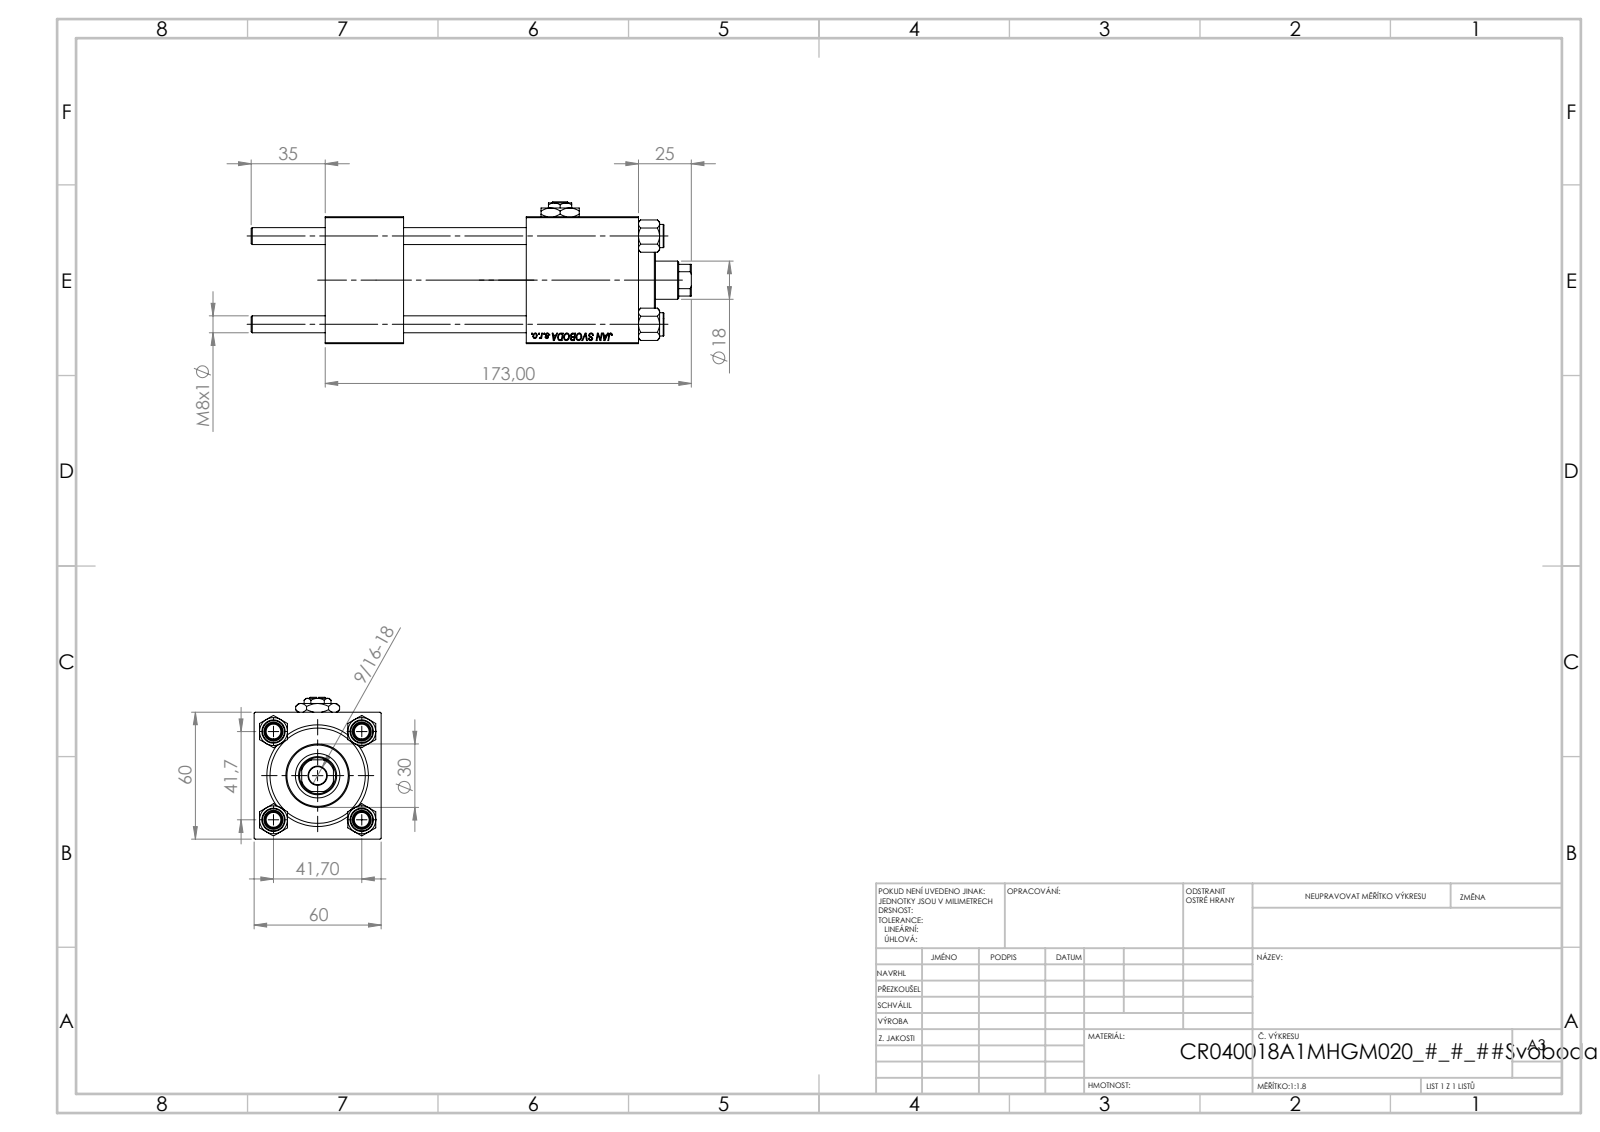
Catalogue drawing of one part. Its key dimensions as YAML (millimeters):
part_name: "V215CR_BODY_A; NUT_M5; Zatka_pro_OIL_PORT; V215_VC_A (+2 more)"
step_written_by: "SolidWorks 2019 (CONFIG_CONTROL_DESIGN)"
units: millimeters
bodies: {solids: 12, faces: 1183, planar: 545, cylindrical: 82, other: 556}
overall_size: [208, 67, 60]
volume: 412009
surface_area: 115273
round_holes:
  - {diameter: 8, count: 4}
  - {diameter: 7, count: 2}
  - {diameter: 16.66, count: 2}
  - {diameter: 24, count: 2}
  - {diameter: 8.5, count: 1}
  - {diameter: 18, count: 1}
  - {diameter: 21, count: 1}
  - {diameter: 31, count: 1}
  - {diameter: 40, count: 1}
  - {diameter: 45, count: 1}
round_bosses_or_shafts:
  - {diameter: 11, count: 4}
  - {diameter: 46, count: 1}
  - {diameter: 30, count: 1}
partial_cylinders:
  - {radius: 8.5, count: 1}
face_to_face_distances: [60, 37, 148, 111, 58, 53, 95, 119.3, 82.3, 24.3]
hole_center_spacings: [29.49, 41.7, 58.97, 92.5]
